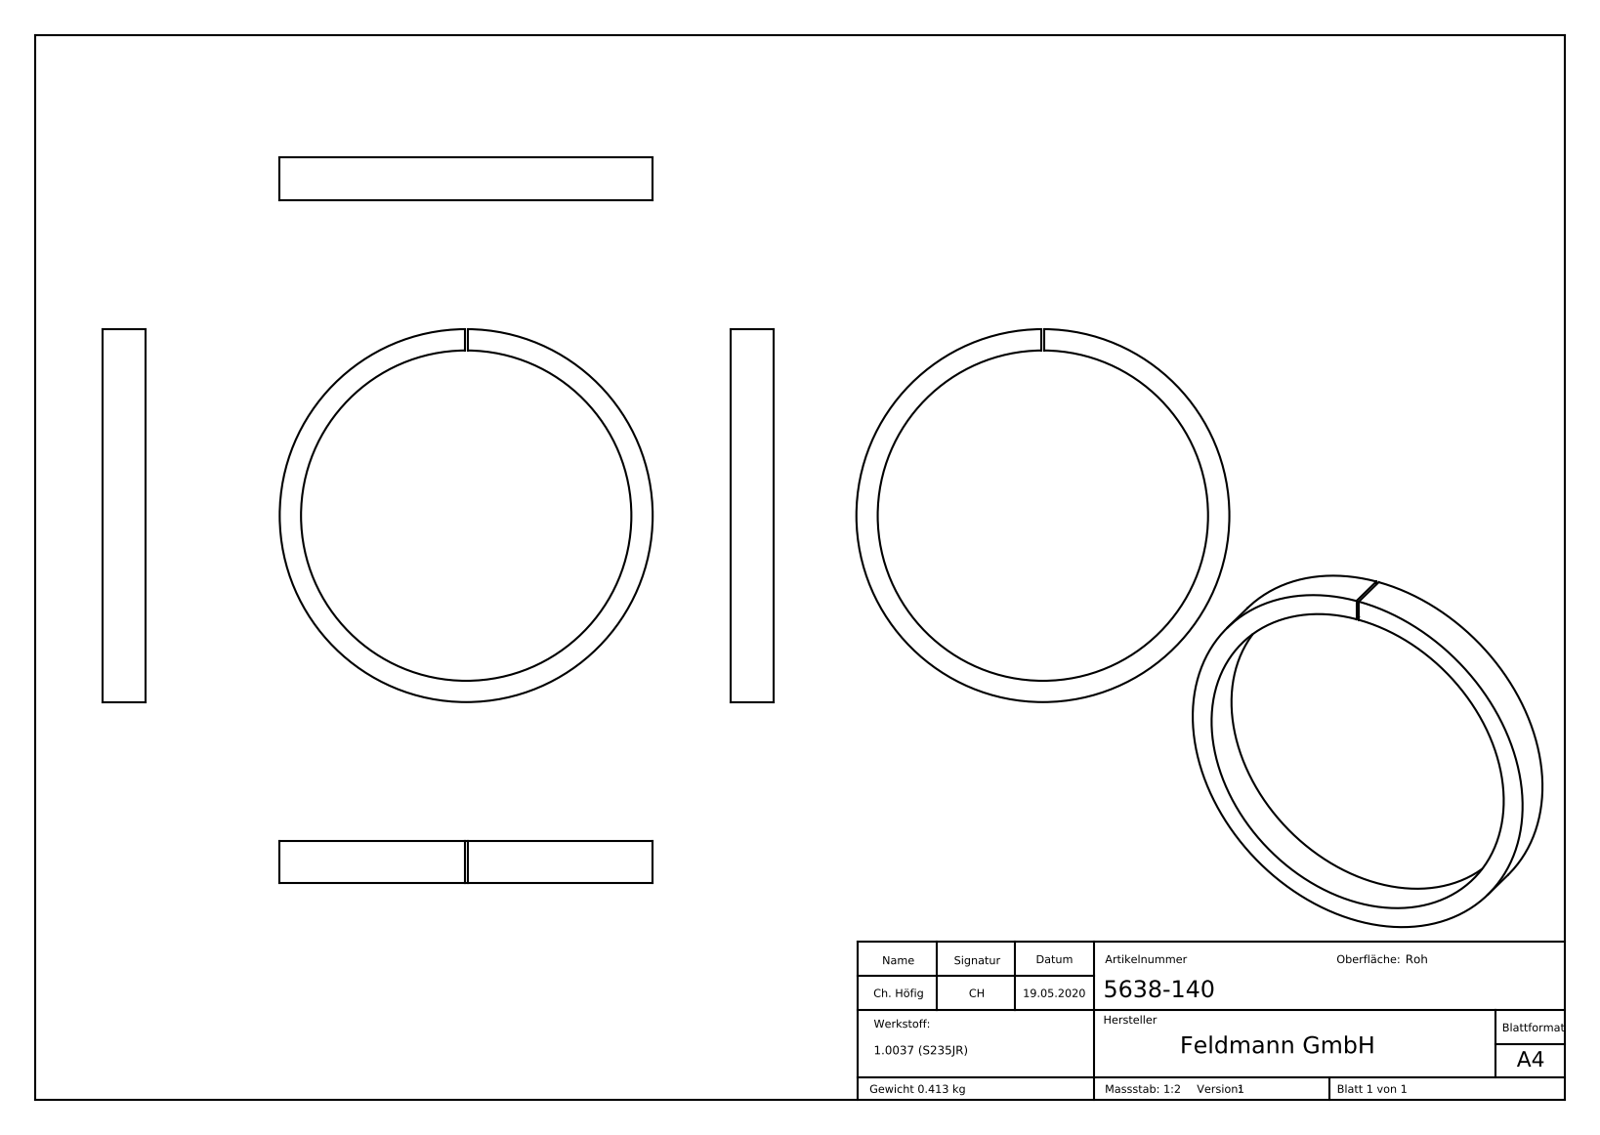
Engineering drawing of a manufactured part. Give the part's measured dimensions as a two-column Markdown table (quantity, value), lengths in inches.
| quantity | value |
| --- | --- |
| part name | 5638-140 |
| STEP written by | SolidWorks 2015 (CONFIG_CONTROL_DESIGN) |
| units | inches |
| bodies | 1 solid, 224 faces (117 planar, 2 cylindrical, 105 other) |
| overall size | 5.512 × 5.512 × 0.63 |
| volume | 3.231 in³ |
| surface area | 31.18 in² |
| round holes (diameter × count) | 4.882 × 1 |
| round bosses / shafts (diameter × count) | 5.512 × 1 |
| main face-to-face distances | 0.63, 0.039, 0.043, 0.083, 0.07, 0.033, 0.03, 0.086, 0.109, 0.103 |
